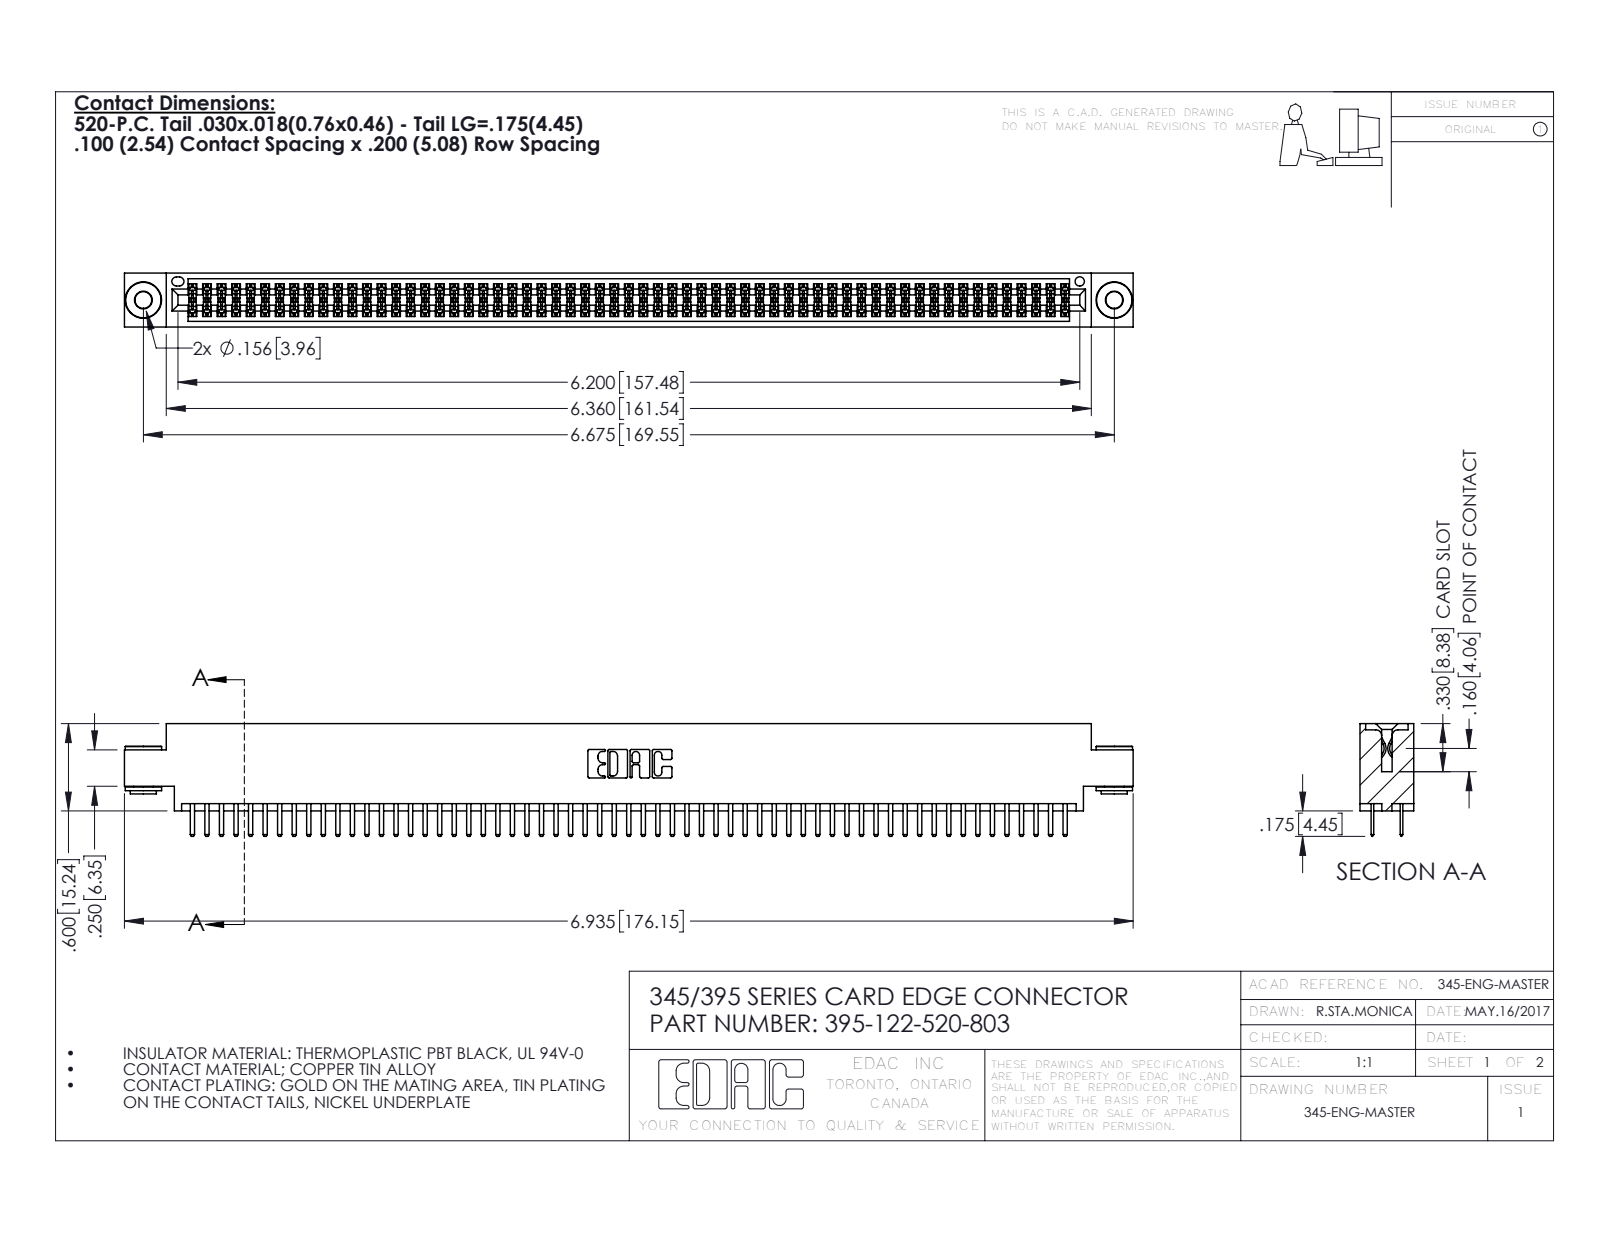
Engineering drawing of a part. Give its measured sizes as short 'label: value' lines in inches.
name: 345-292-001_345-293-120; 345-250-002_345-250-002-102; 345 Part_0.170 Offset - 0.156 Dia-TH; 395-122-520-803
written by: SolidWorks 2016 (CONFIG_CONTROL_DESIGN)
unit: in
bodies: 125 solids, 6756 faces (4364 planar, 2384 cylindrical, 8 other)
size: 6.935 × 0.775 × 0.37
volume: 1.046 in³; area: 40.2 in²
holes: 2× ⌀0.116, 2× ⌀0.156, 1× ⌀0.064
bosses: 2× ⌀0.25, 2× ⌀0.18, 2× ⌀0.136
rounds: 183× R0.006, 126× R0.01, 22× R0.01, 6× R0.007, 6× R0.031, 3× R0.026, 2× R0.014, 2× R0.019
face distances: 0.072, 0.298, 0.2, 0.37, 0.098, 0.272, 0.025, 0.225, 0.022, 0.175
hole spacings: 0.27, 6.439, 6.675
